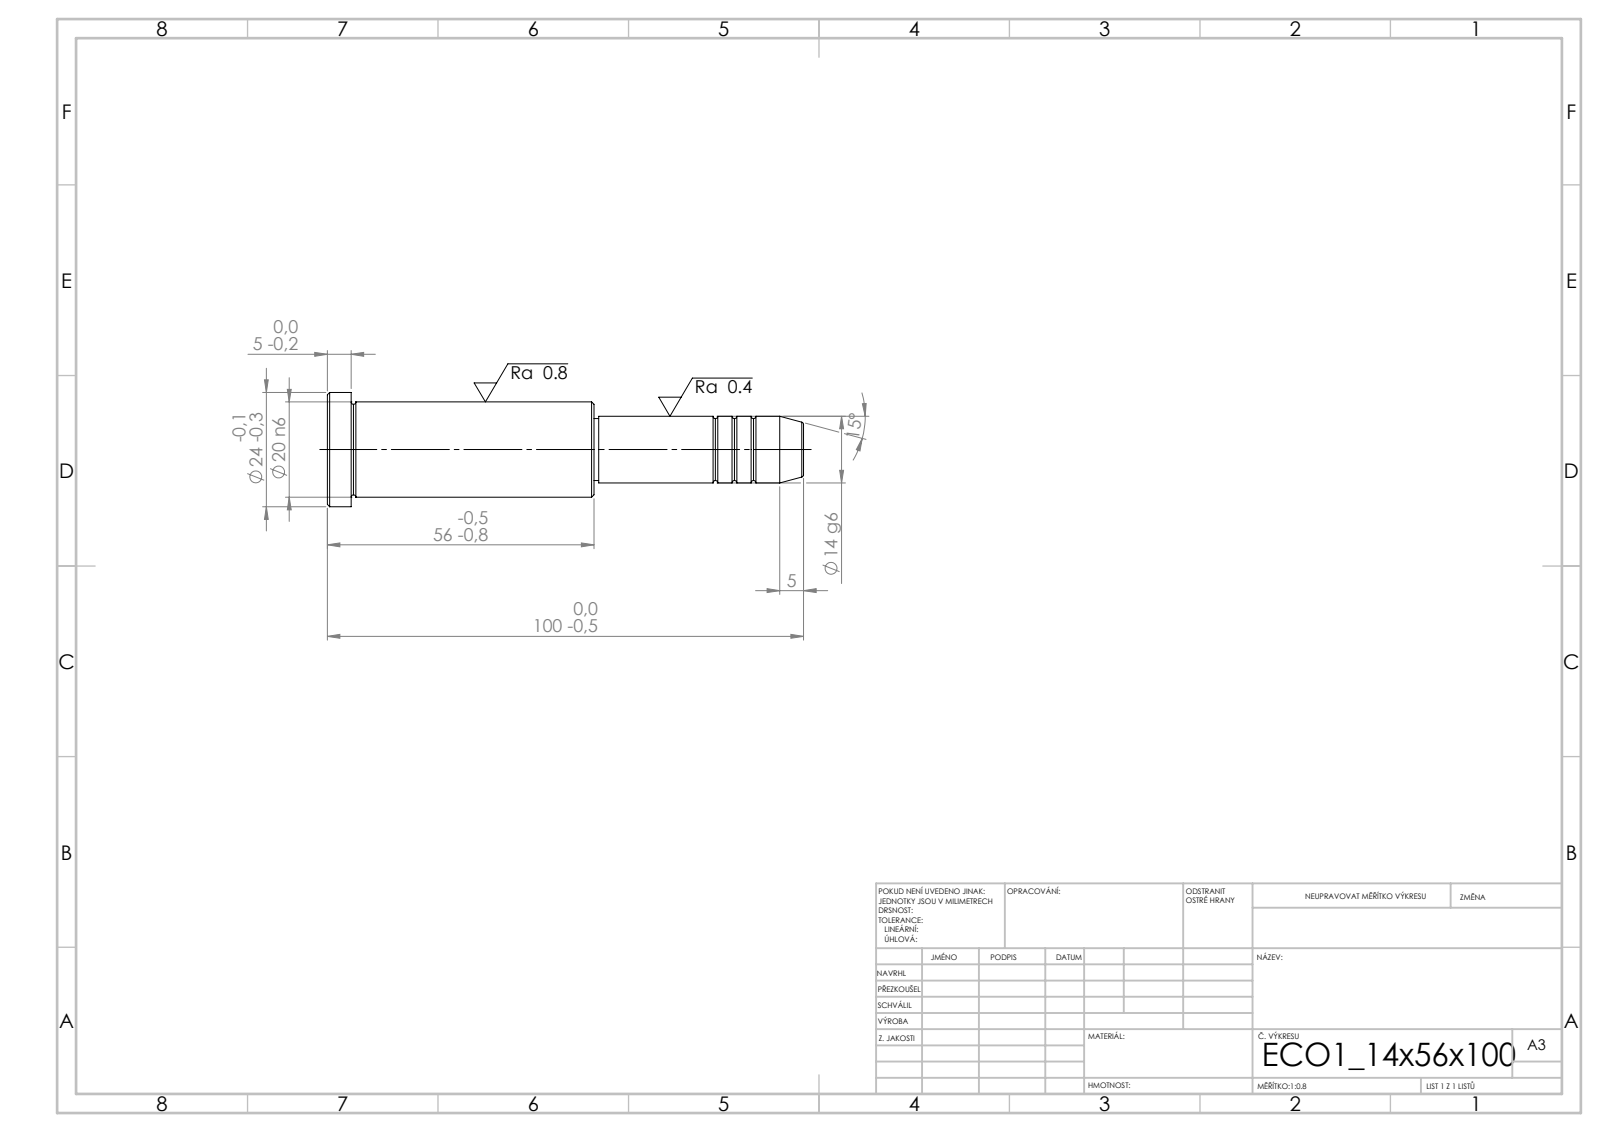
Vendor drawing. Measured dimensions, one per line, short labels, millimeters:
written by: SolidWorks 2019 (CONFIG_CONTROL_DESIGN)
unit: mm
bodies: 1 solid, 43 faces (5 planar, 14 cylindrical, 24 other)
size: 100 × 24 × 24
volume: 24 806 mm³; area: 6 447 mm²
bosses: 1× ⌀24, 1× ⌀20, 1× ⌀14, 1× ⌀13
face distances: 56, 51, 5, 44, 95, 100, 43, 1, 52, 57
